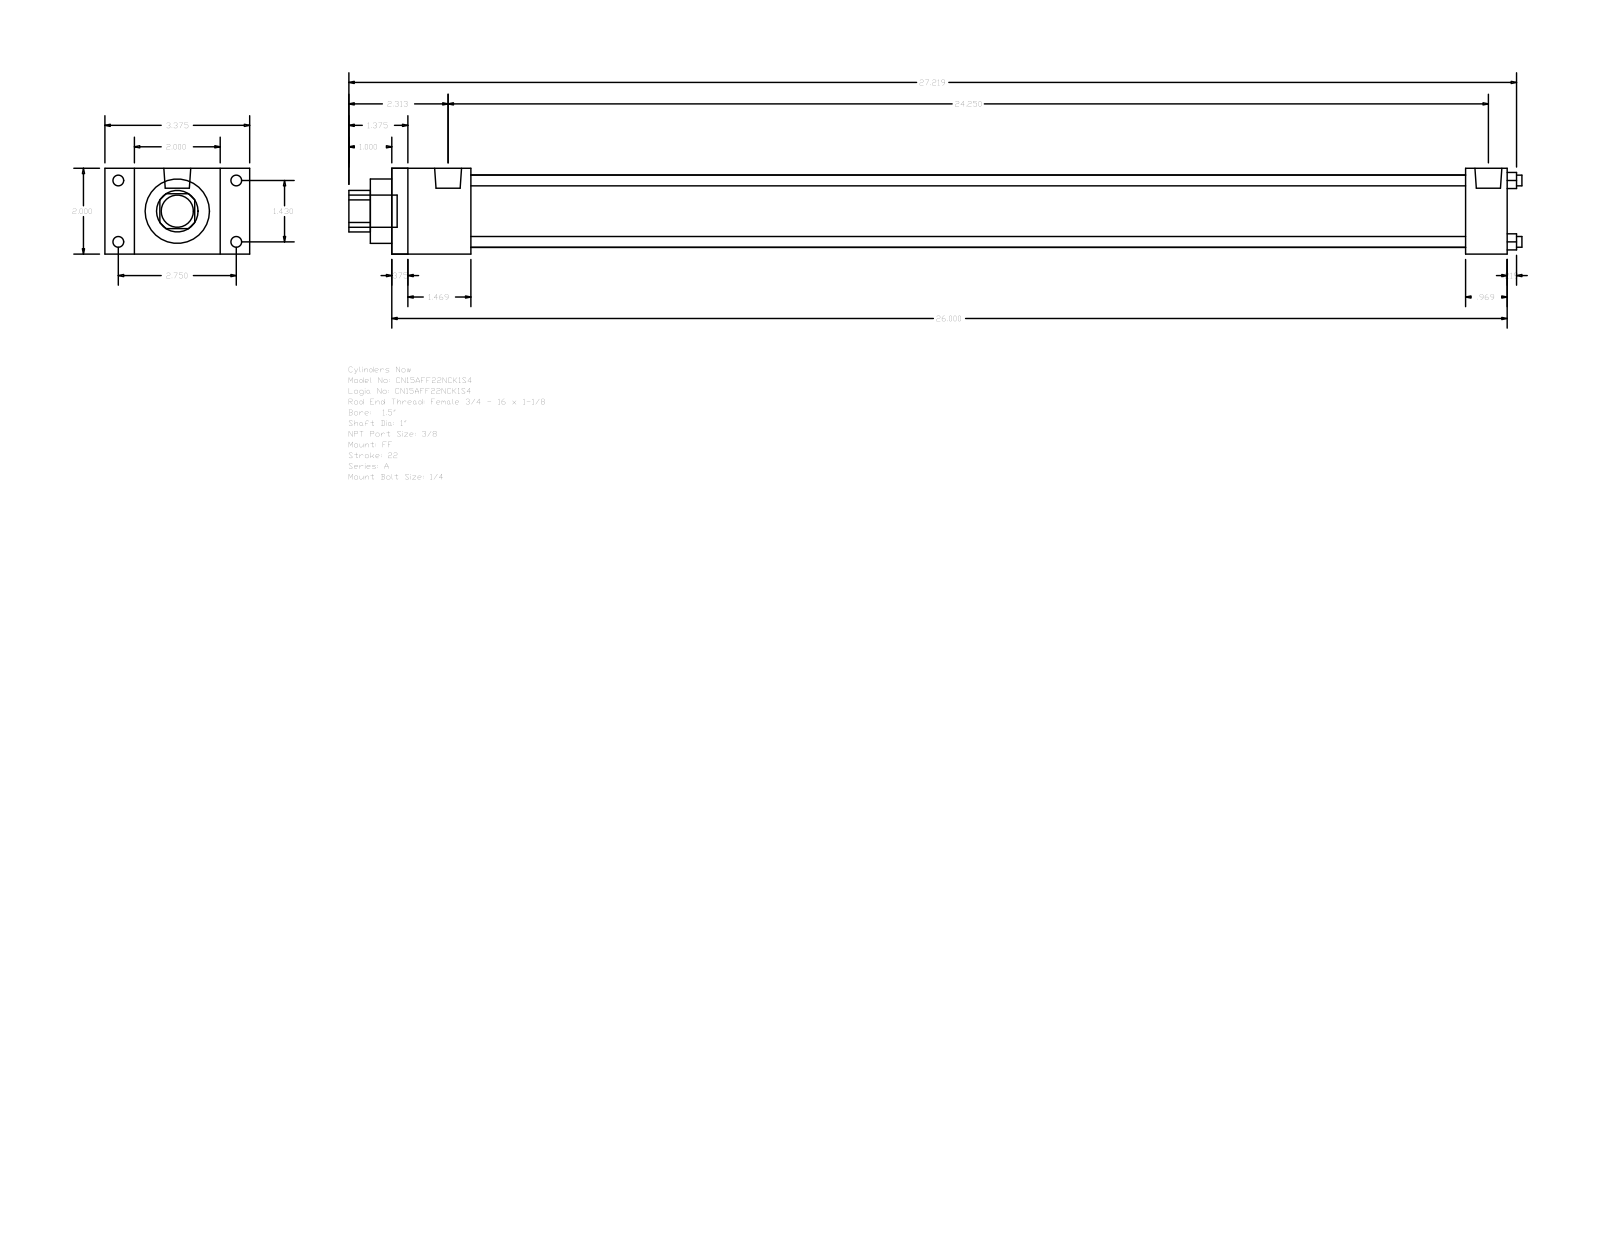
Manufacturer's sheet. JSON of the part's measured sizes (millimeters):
{"part_name": "A_FF__0150_1", "step_written_by": "GSSL Pune (CONFIG_CONTROL_DESIGN)", "units": "millimeters", "bodies": {"solids": 0, "faces": 92, "planar": 64, "cylindrical": 28, "other": 0}, "overall_size": [694.53, 85.72, 50.8], "round_holes": [[6.35, 4], [25.4, 1], [38.1, 1], [42.93, 1]], "round_bosses_or_shafts": [[6.35, 4], [5.56, 4], [15.93, 2], [19.05, 1]], "partial_cylinders_radius": [[12.29, 1]], "face_to_face_distances": [50.8, 660.4, 9.52, 650.88, 46.83, 635.79, 37.31, 626.27, 588.96, 613.57], "hole_center_spacings": [25.68, 36.32, 51.36]}
